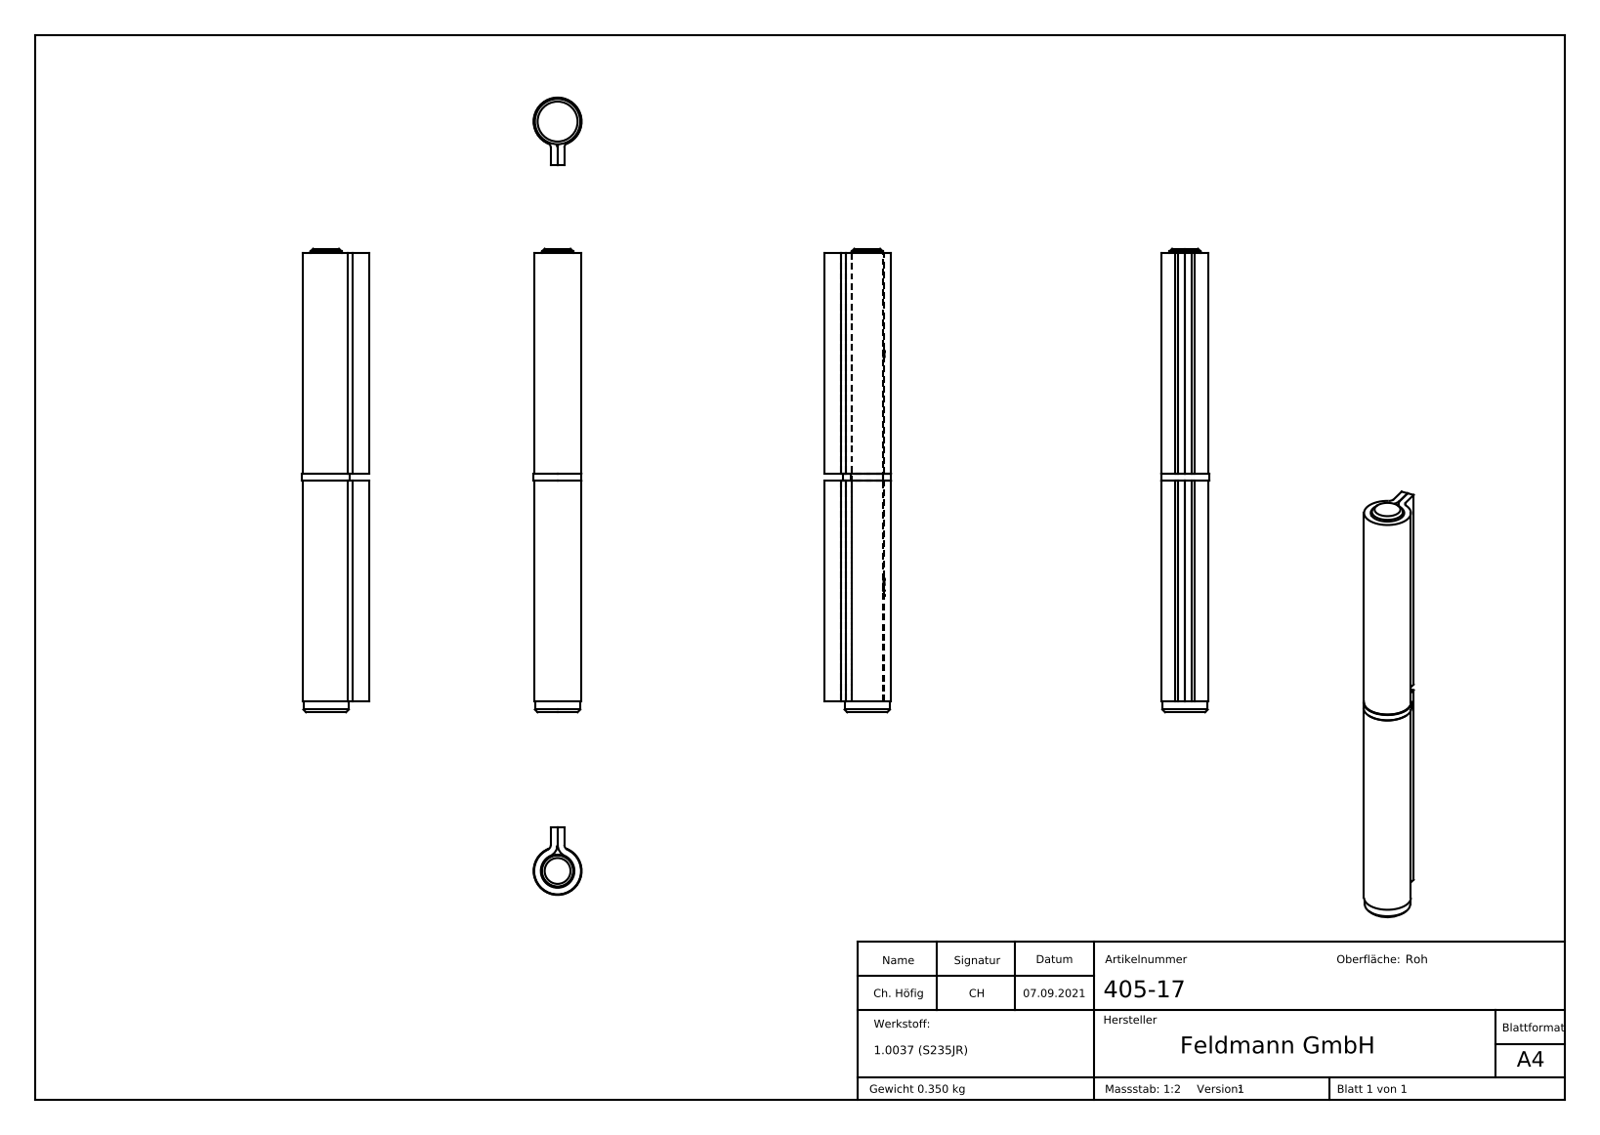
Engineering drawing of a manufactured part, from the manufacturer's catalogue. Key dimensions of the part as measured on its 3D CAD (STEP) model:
Part name (STEP PRODUCT): 405-xx Teil4; 405-xx Teil1_405-17 Teil1; 405-xx Teil3; 405-xx Teil2_405-17 Teil2 (+5 more)
STEP written by: SolidWorks 2018 (CONFIG_CONTROL_DESIGN)
Units: millimetres
Bodies: 4 solids, 302 faces (154 planar, 37 cylindrical, 111 other)
Overall size (bounding box): 174 × 25.2 × 18
Volume: 44 837 mm³ · Surface area: 29 094 mm²
Round holes (diameter × count): ⌀12 ×1, ⌀12.6 ×1
Round bosses / shafts (diameter × count): ⌀18 ×1, ⌀17.6 ×1, ⌀17 ×1, ⌀11.7 ×1
Partial cylindrical surfaces — rounded edges, fillets, slot ends (radius × count): R2 ×2, R4.5 ×2, R6.4 ×1
Main face-to-face distances: 2.5, 2.6, 5.1, 85.5, 83, 87, 4, 89.5, 172.5, 168.5
